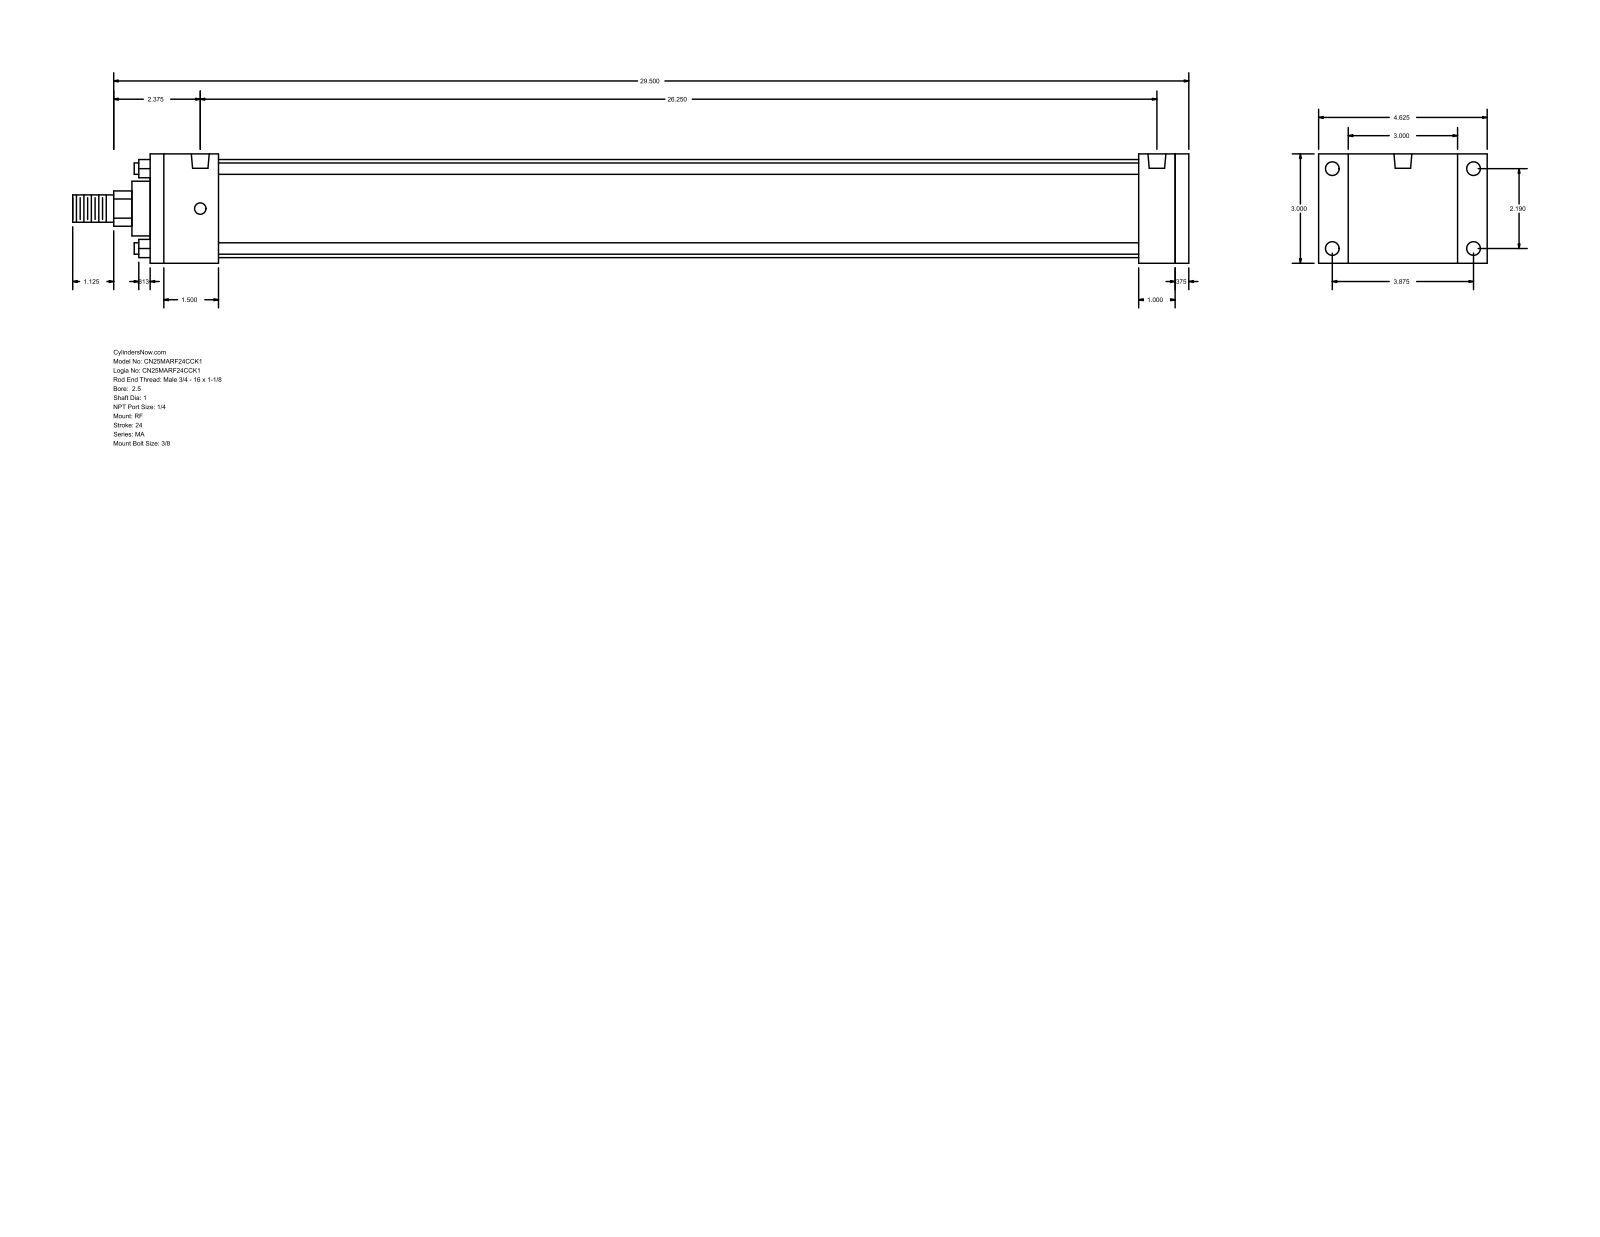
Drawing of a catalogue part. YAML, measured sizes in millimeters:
part_name: "MA_RF__0250_1"
step_written_by: "GSSL Pune (CONFIG_CONTROL_DESIGN)"
units: millimeters
bodies: {solids: 0, faces: 92, planar: 64, cylindrical: 28, other: 0}
overall_size: [777.88, 117.47, 76.2]
round_holes:
  - {diameter: 7.94, count: 4}
  - {diameter: 9.53, count: 4}
  - {diameter: 12.49, count: 2}
round_bosses_or_shafts:
  - {diameter: 7.94, count: 4}
  - {diameter: 68.33, count: 1}
  - {diameter: 38.1, count: 1}
  - {diameter: 25.4, count: 1}
  - {diameter: 19.05, count: 1}
partial_cylinders:
  - {radius: 12.29, count: 1}
face_to_face_distances: [76.2, 723.9, 9.53, 714.37, 47.63, 688.98, 641.35, 666.74, 676.27, 25.39]
hole_center_spacings: [55.62, 98.42, 113.05, 666.75]
